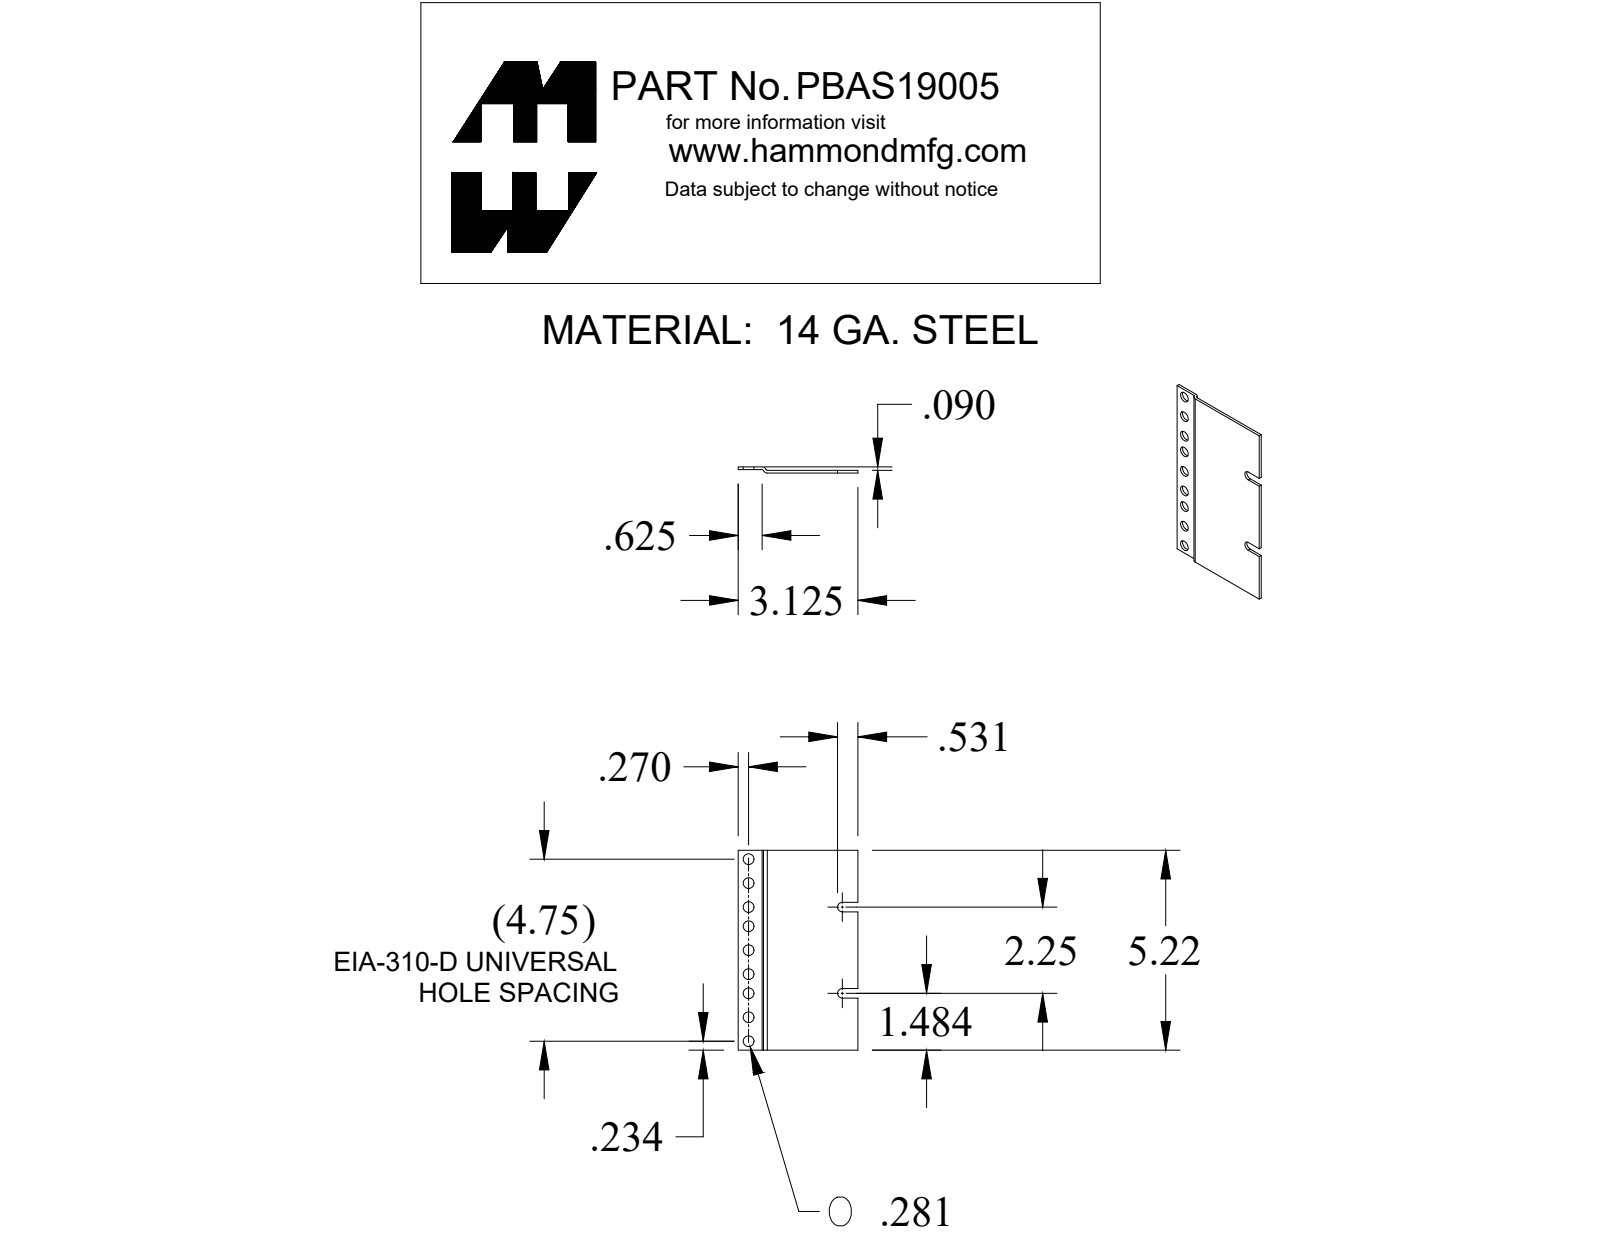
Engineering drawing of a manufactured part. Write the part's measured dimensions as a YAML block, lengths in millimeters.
part_name: "PBAS19005BK2"
step_written_by: "SolidWorks 2019 (CONFIG_CONTROL_DESIGN)"
units: millimeters
bodies: {solids: 1, faces: 29, planar: 14, cylindrical: 15, other: 0}
overall_size: [132.5, 79.4, 4.1]
volume: 18520
surface_area: 21480
round_holes:
  - {diameter: 7.1, count: 9}
partial_cylinders:
  - {radius: 0.9, count: 2}
  - {radius: 2.7, count: 2}
  - {radius: 3.2, count: 2}
face_to_face_distances: [1.8, 2.3, 4.1, 0.5, 2.3, 1.8, 79.4, 132.5, 34.5, 98]
hole_center_spacings: [15.9, 28.6, 44.5, 12.7, 15.9, 31.8, 44.5, 60.3]
